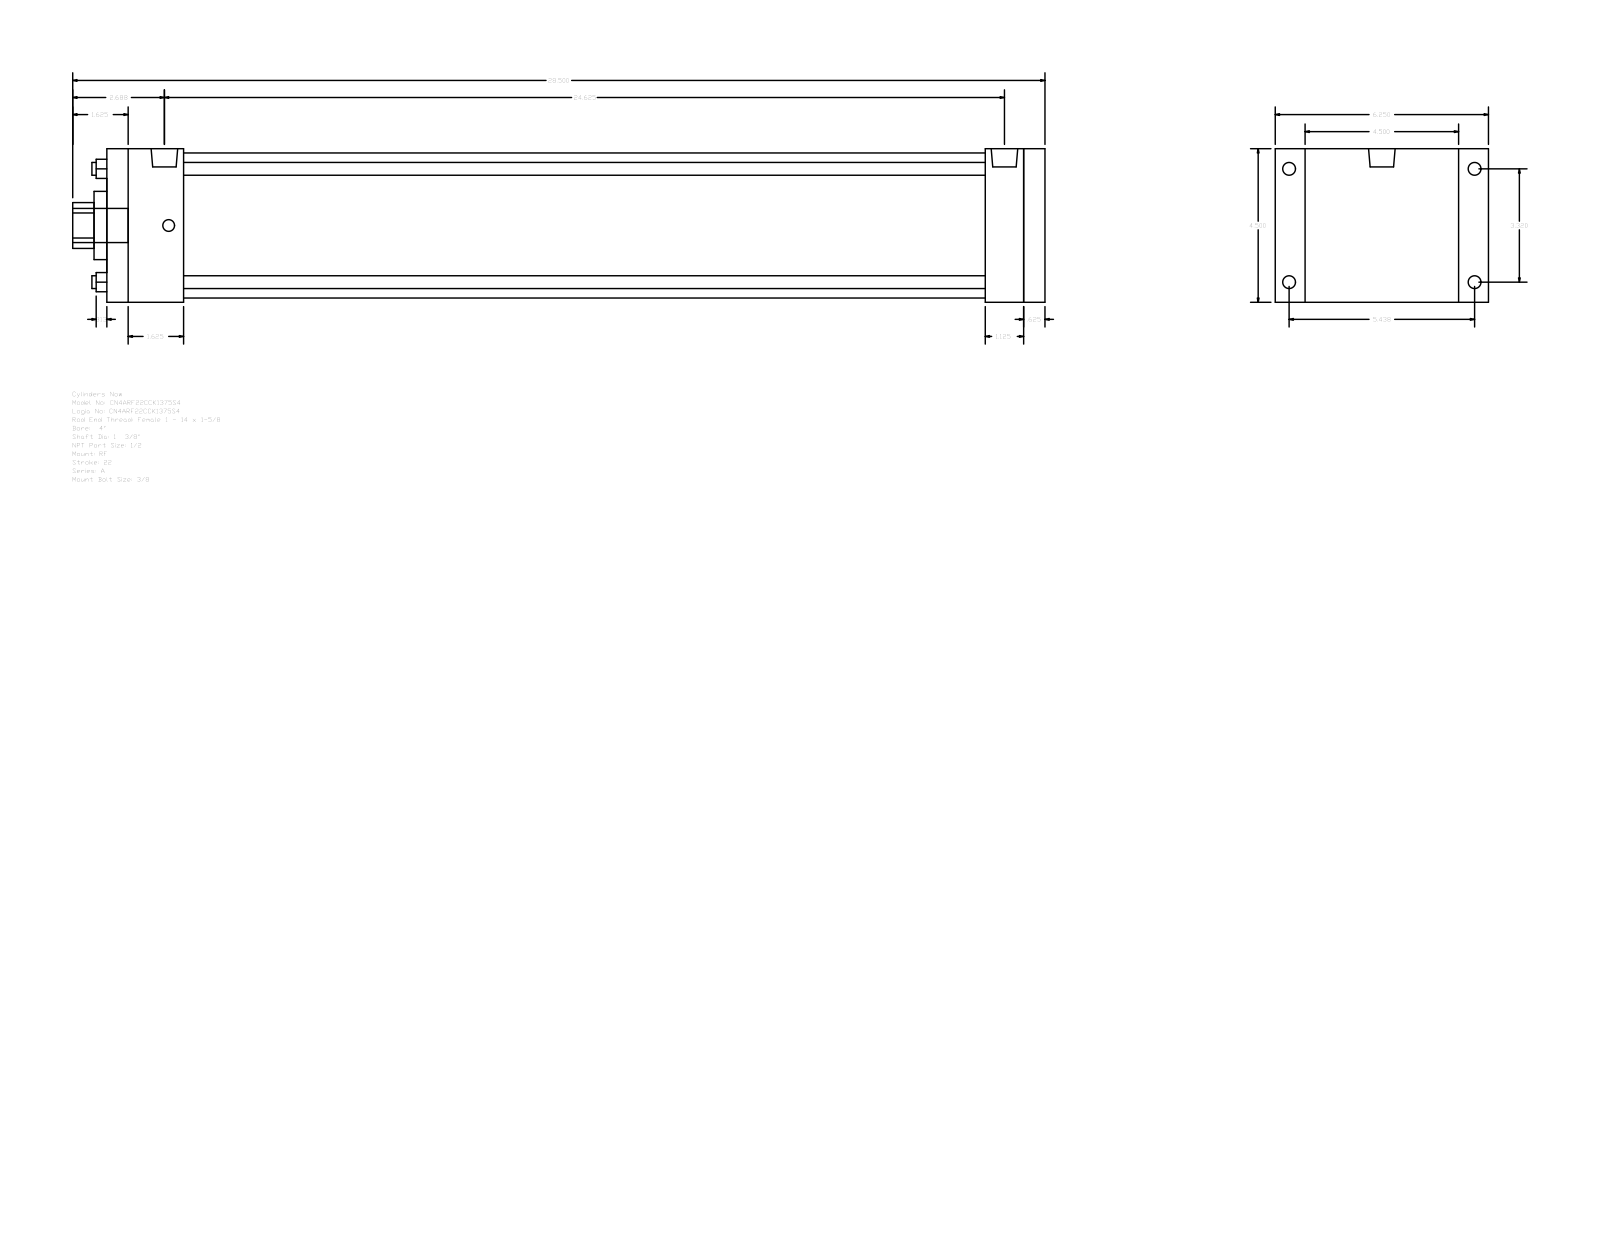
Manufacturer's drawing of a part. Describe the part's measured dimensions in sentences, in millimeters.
The part is named "A_RF__0400_1.375". Its 3-D file was written by "GSSL Pune (CONFIG_CONTROL_DESIGN)". It is 0 solids with 92 faces: 64 planar, 28 cylindrical and 0 other. Overall it measures 723.9 by 158.75 by 114.3 millimeters. Round holes: 4 of diameter 9.53, 1 of diameter 34.92, 1 of diameter 50.8, 1 of diameter 107.95. Round bosses or shafts: 4 of diameter 9.53, 4 of diameter 8.73, 2 of diameter 19.77, 1 of diameter 25.4. Partial cylindrical surfaces (rounded edges, fillets, slot ends): 1 of radius 17.06. The main face-to-face distances are 114.3, 698.5, 15.88, 682.62, 28.57, 22.23, 136.53, 654.05, 44.45, 57.15. The hole center spacings are 59.62, 84.32, 119.25.
